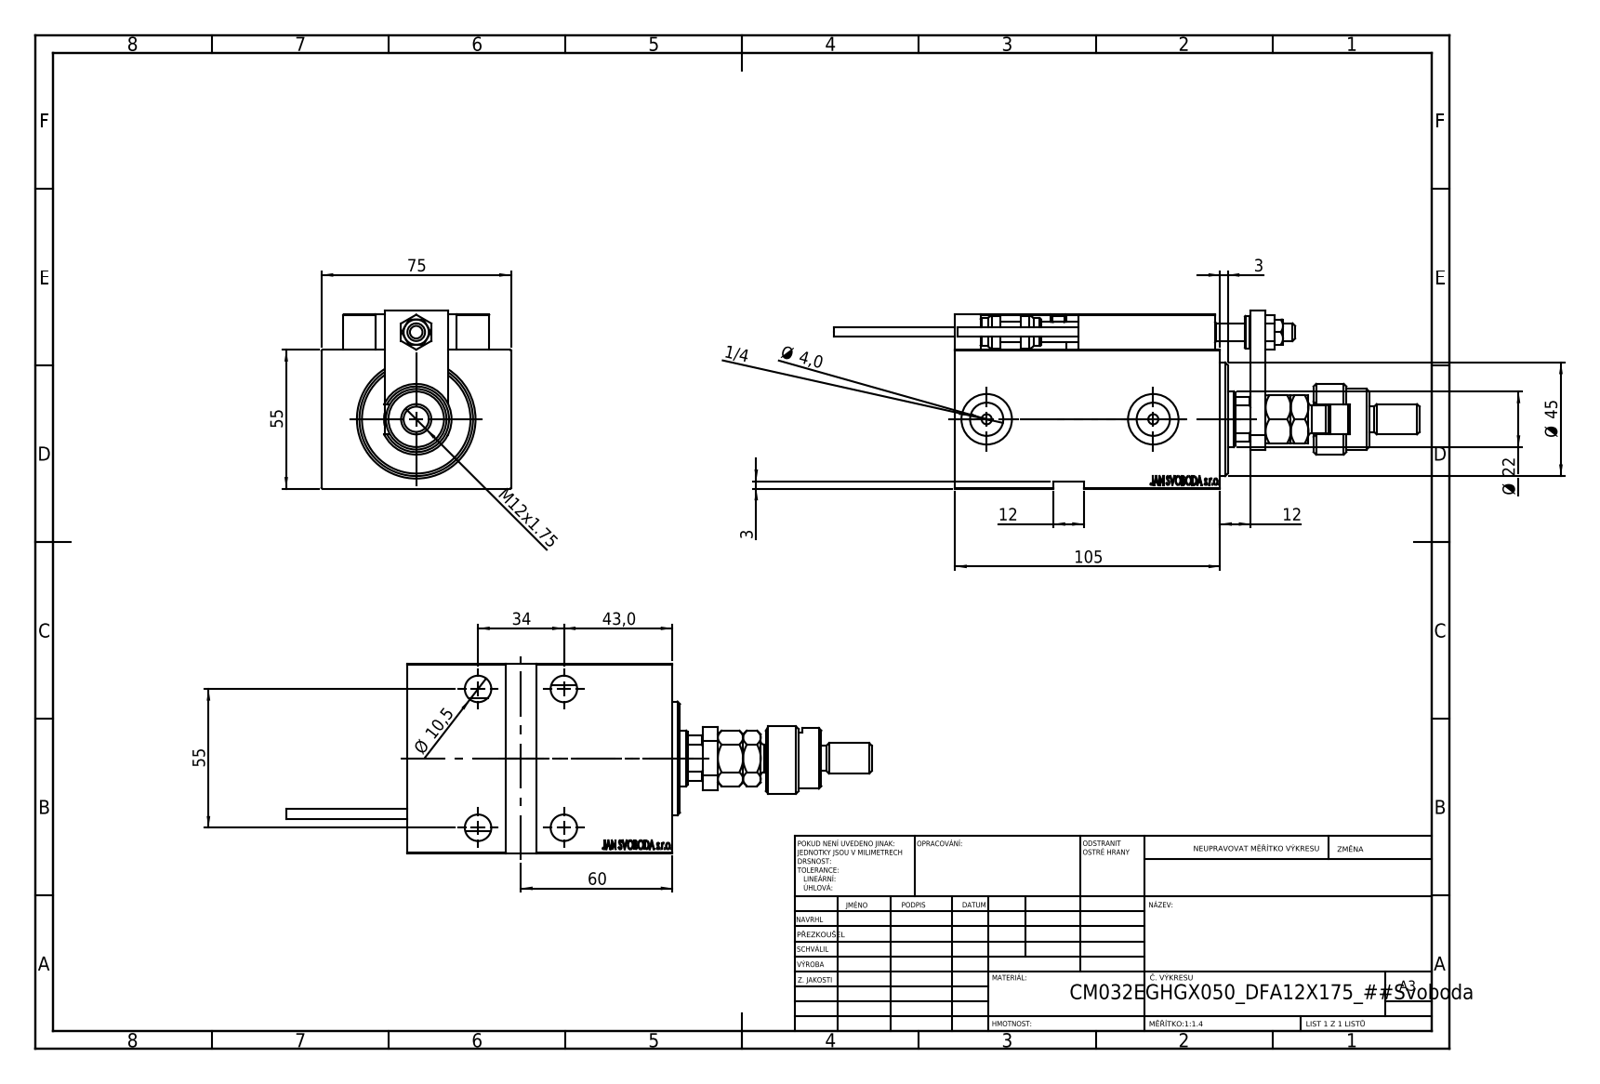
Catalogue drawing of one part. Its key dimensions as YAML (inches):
part_name: "V450CM_VC_B; MFA; Block; ALLEN BOLT D5 (+7 more)"
step_written_by: "SolidWorks 2019 (CONFIG_CONTROL_DESIGN)"
units: inches
bodies: {solids: 26, faces: 1375, planar: 597, cylindrical: 193, other: 585}
overall_size: [9.134, 2.953, 2.776]
volume: 27.72
surface_area: 160.6
round_holes:
  - {diameter: 0.157, count: 6}
  - {diameter: 0.315, count: 5}
  - {diameter: 0.413, count: 5}
  - {diameter: 0.65, count: 5}
  - {diameter: 0.126, count: 4}
  - {diameter: 0.197, count: 2}
  - {diameter: 0.518, count: 2}
  - {diameter: 0.787, count: 2}
  - {diameter: 0.276, count: 1}
  - {diameter: 0.866, count: 1}
  - {diameter: 1.004, count: 1}
  - {diameter: 1.26, count: 1}
round_bosses_or_shafts:
  - {diameter: 0.433, count: 2}
  - {diameter: 0.197, count: 2}
  - {diameter: 0.15, count: 2}
  - {diameter: 1.339, count: 1}
  - {diameter: 1.102, count: 1}
  - {diameter: 0.945, count: 1}
  - {diameter: 0.709, count: 1}
  - {diameter: 0.512, count: 1}
partial_cylinders:
  - {radius: 0.012, count: 30}
  - {radius: 0.118, count: 2}
  - {radius: 0.384, count: 1}
  - {radius: 0.413, count: 1}
face_to_face_distances: [2.165, 2.953, 0.394, 0.118, 0.551, 4.134, 2.717, 0.709, 0.984, 0.472]
hole_center_spacings: [0.448, 0.787, 1.138, 1.165, 1.169, 1.339, 1.42, 1.576]
